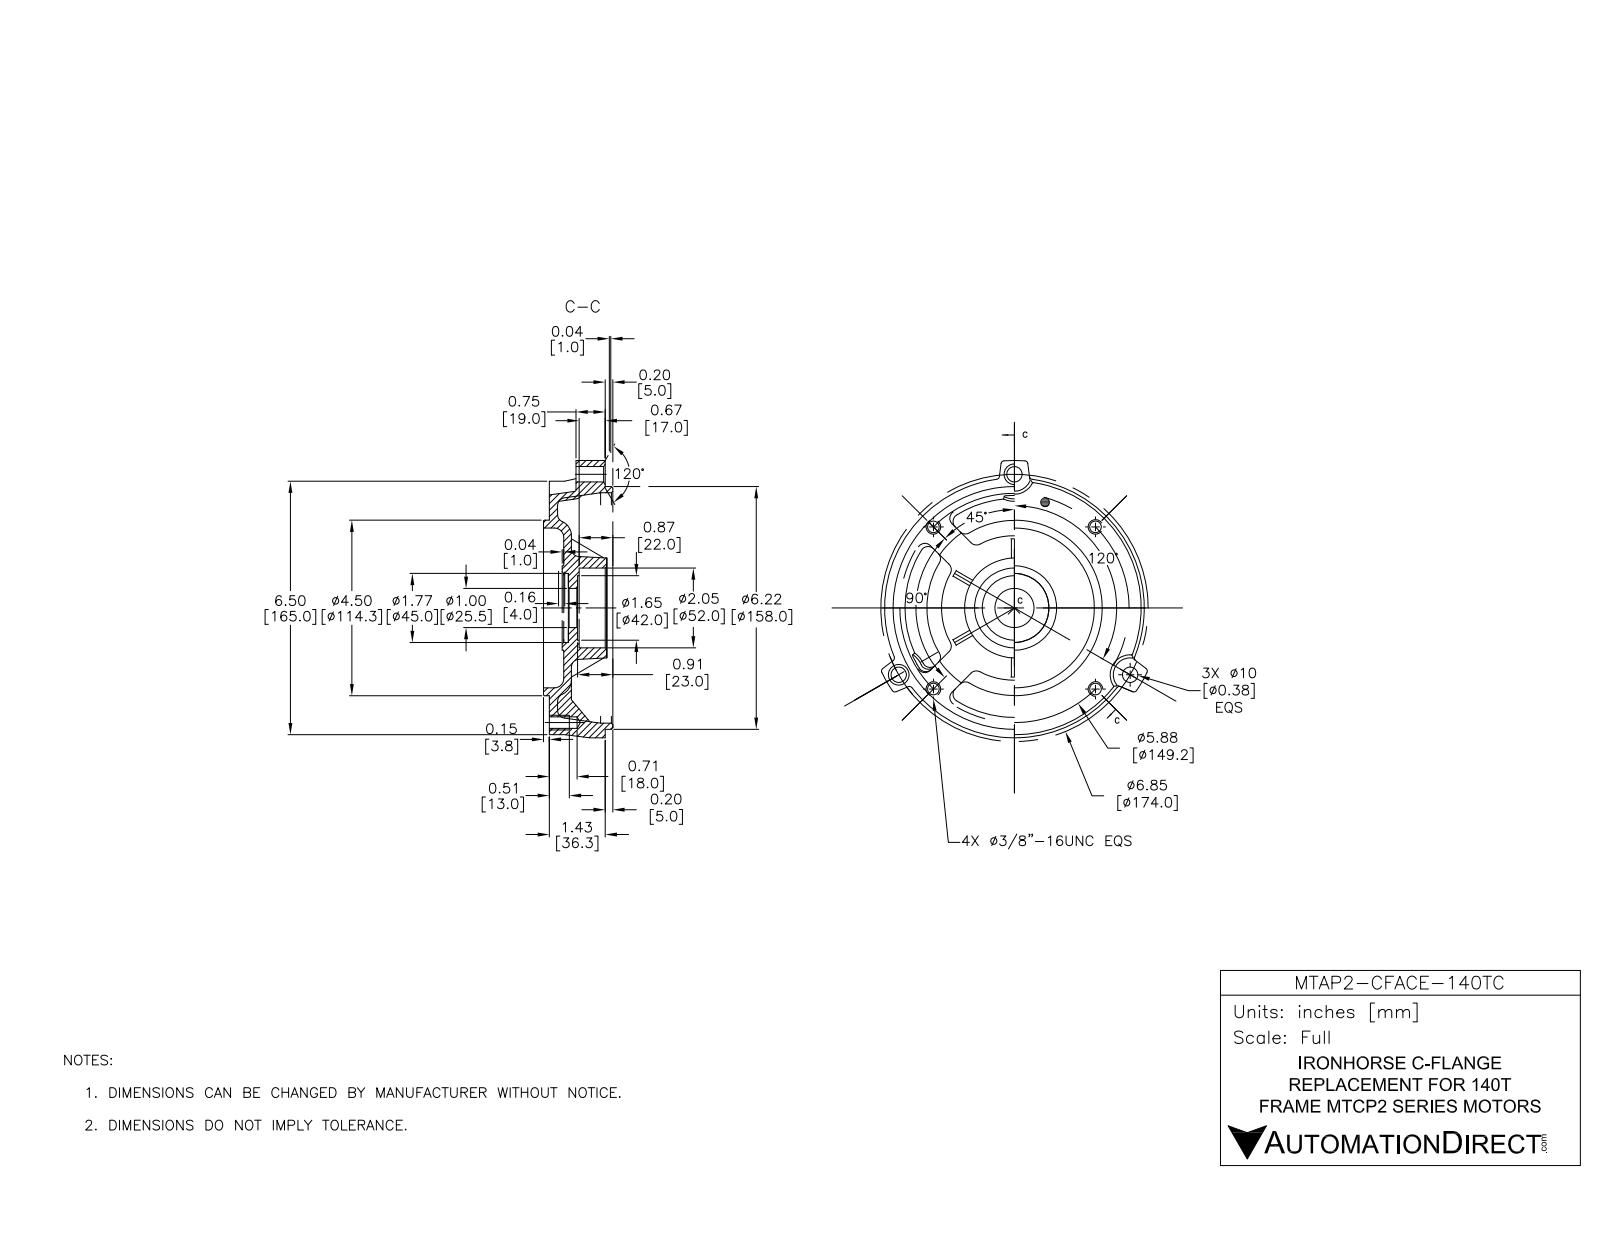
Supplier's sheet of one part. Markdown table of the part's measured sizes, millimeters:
| quantity | value |
| --- | --- |
| part name | MTAP2-CFACE-140TC |
| STEP written by | SolidWorks 2017 (AUTOMOTIVE_DESIGN) |
| units | millimeters |
| bodies | 1 solid, 222 faces (48 planar, 74 cylindrical, 100 other) |
| overall size | 180.5 × 172.5 × 45.1 |
| volume | 347 600 mm³ |
| surface area | 99 610 mm² |
| round holes (diameter × count) | 8 × 4, 10 × 3, 25.5 × 1, 42 × 1, 45 × 1, 52 × 1, 104 × 1, 150 × 1 |
| round bosses / shafts (diameter × count) | 169 × 1, 165 × 1, 158 × 1, 114.3 × 1, 55 × 1 |
| partial cylindrical surfaces (radius × count) | 3 × 12, 2.5 × 6, 5 × 6, 96 × 1 |
| main face-to-face distances | 5, 27, 4, 9.1, 22, 1, 36.1, 41.1, 14.1, 18.1 |
| hole center spacings | 74.6, 105.5, 87, 24.4, 62.9, 98.9, 128.4, 149.2 |
